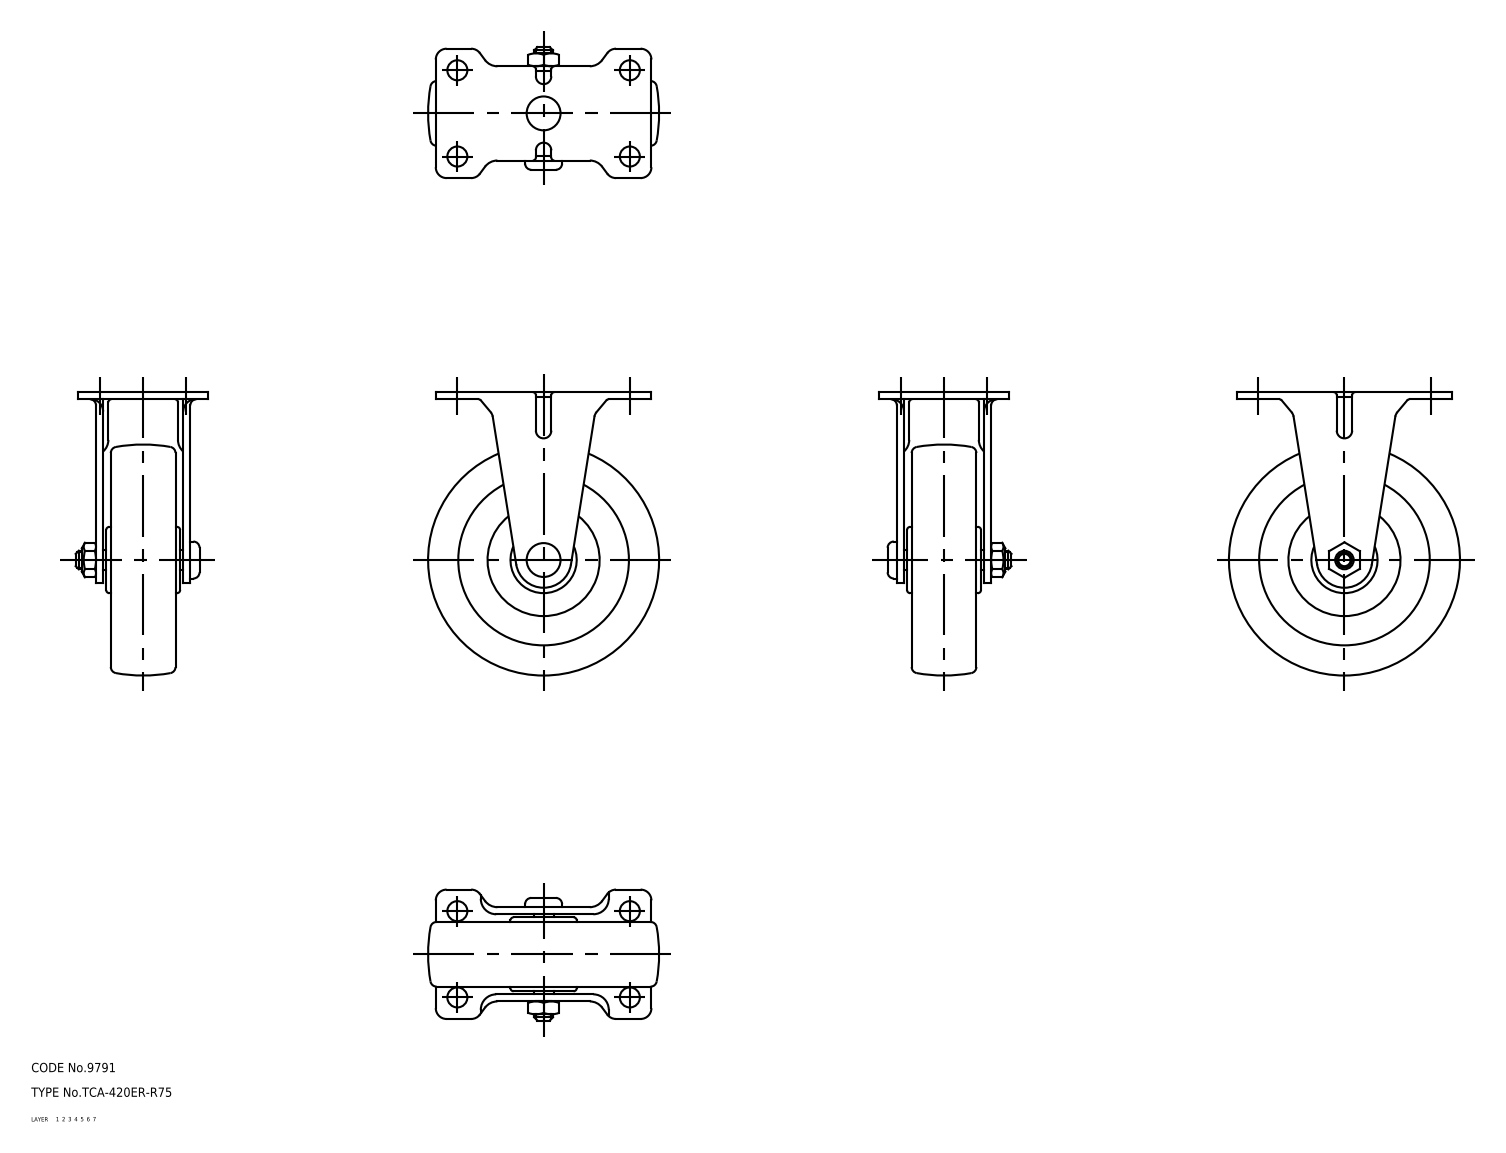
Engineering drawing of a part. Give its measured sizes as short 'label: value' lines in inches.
name: wheel; axle; No_420_ER_R75_3_30826_36
written by: CADfix (AUTOMOTIVE_DESIGN)
unit: in
bodies: 3 solids, 172 faces (0 planar, 0 cylindrical, 172 other)
size: 3.622 × 2.953 × 1.689
volume: 6.178 in³; area: 41.83 in²
